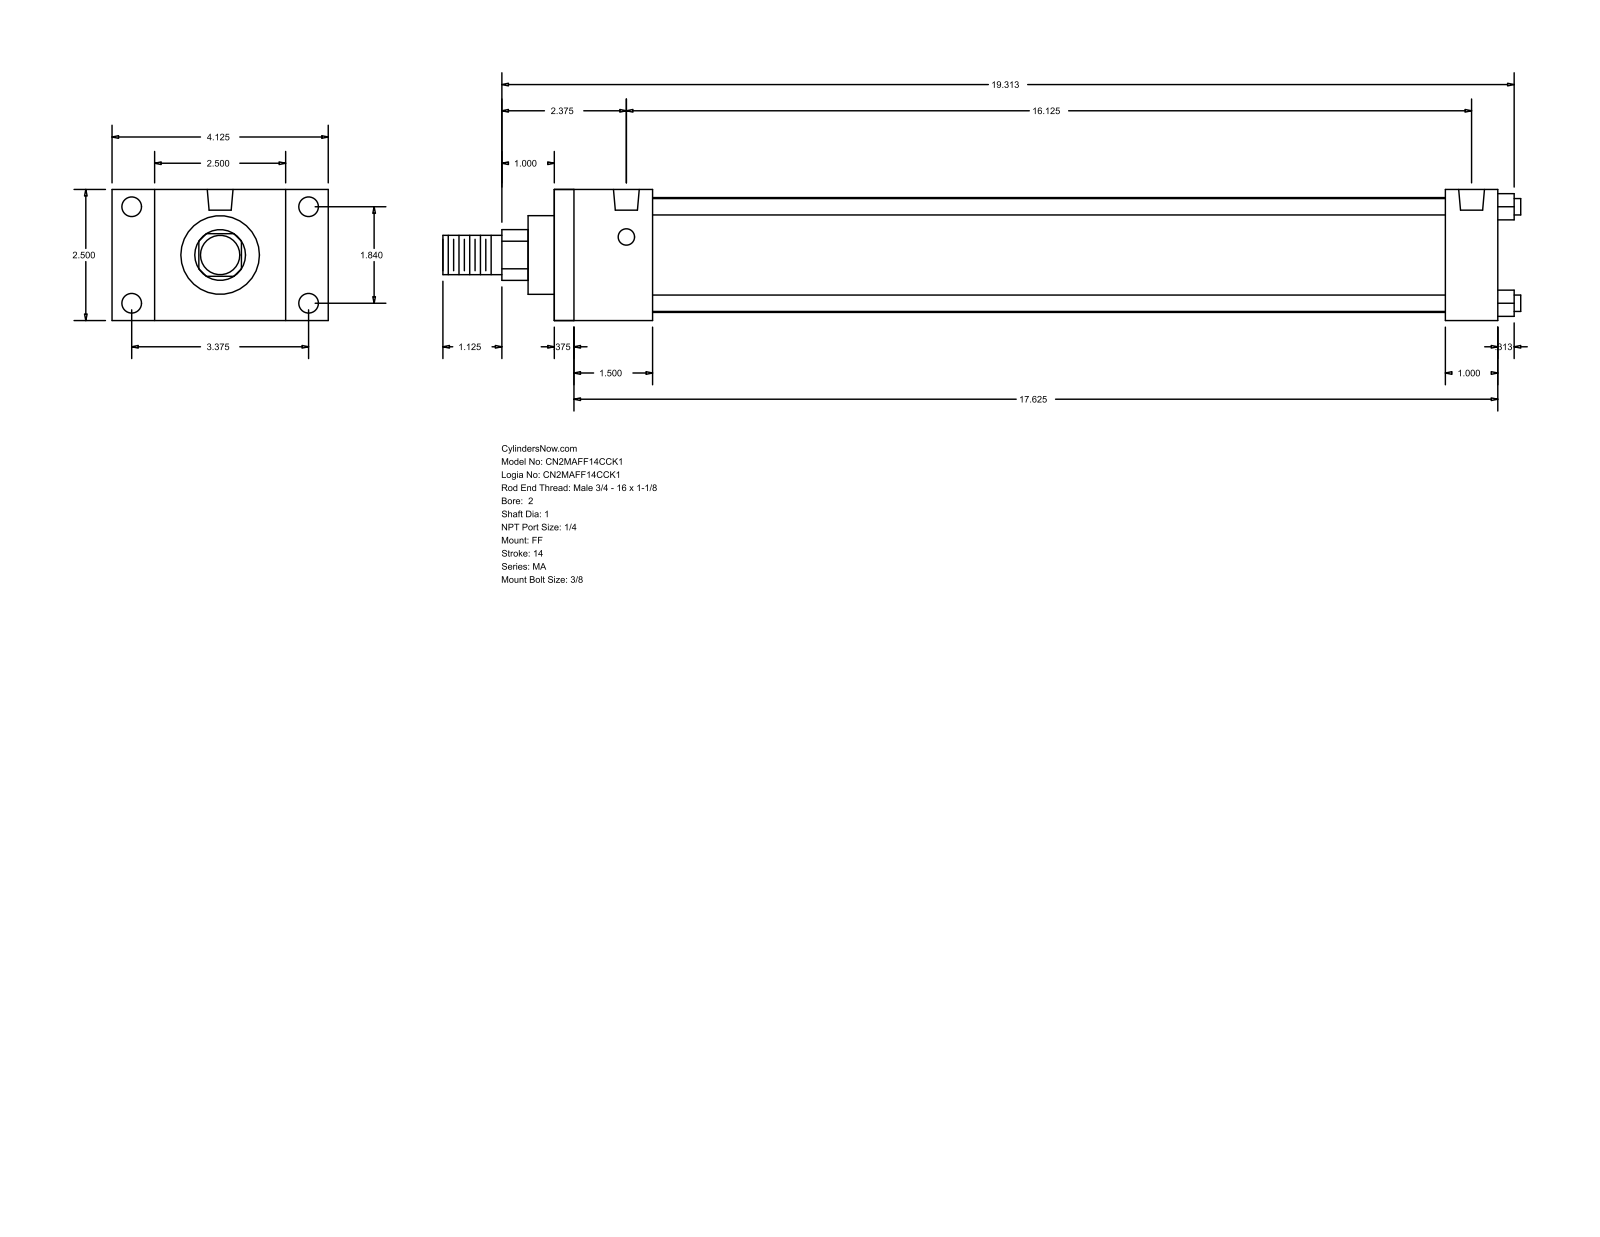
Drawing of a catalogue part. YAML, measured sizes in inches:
part_name: "MA_FF__0200_1"
step_written_by: "GSSL Pune (CONFIG_CONTROL_DESIGN)"
units: inches
bodies: {solids: 0, faces: 92, planar: 64, cylindrical: 28, other: 0}
overall_size: [20.563, 4.125, 2.5]
round_holes:
  - {diameter: 0.313, count: 4}
  - {diameter: 0.375, count: 4}
  - {diameter: 0.492, count: 2}
round_bosses_or_shafts:
  - {diameter: 0.313, count: 4}
  - {diameter: 2.19, count: 1}
  - {diameter: 1.5, count: 1}
  - {diameter: 1, count: 1}
  - {diameter: 0.75, count: 1}
partial_cylinders:
  - {radius: 0.484, count: 1}
face_to_face_distances: [2.5, 18, 0.375, 17.625, 1, 0.813, 0.5, 1.875, 17, 1.5]
hole_center_spacings: [1.84, 3.375, 3.844, 16.125]
